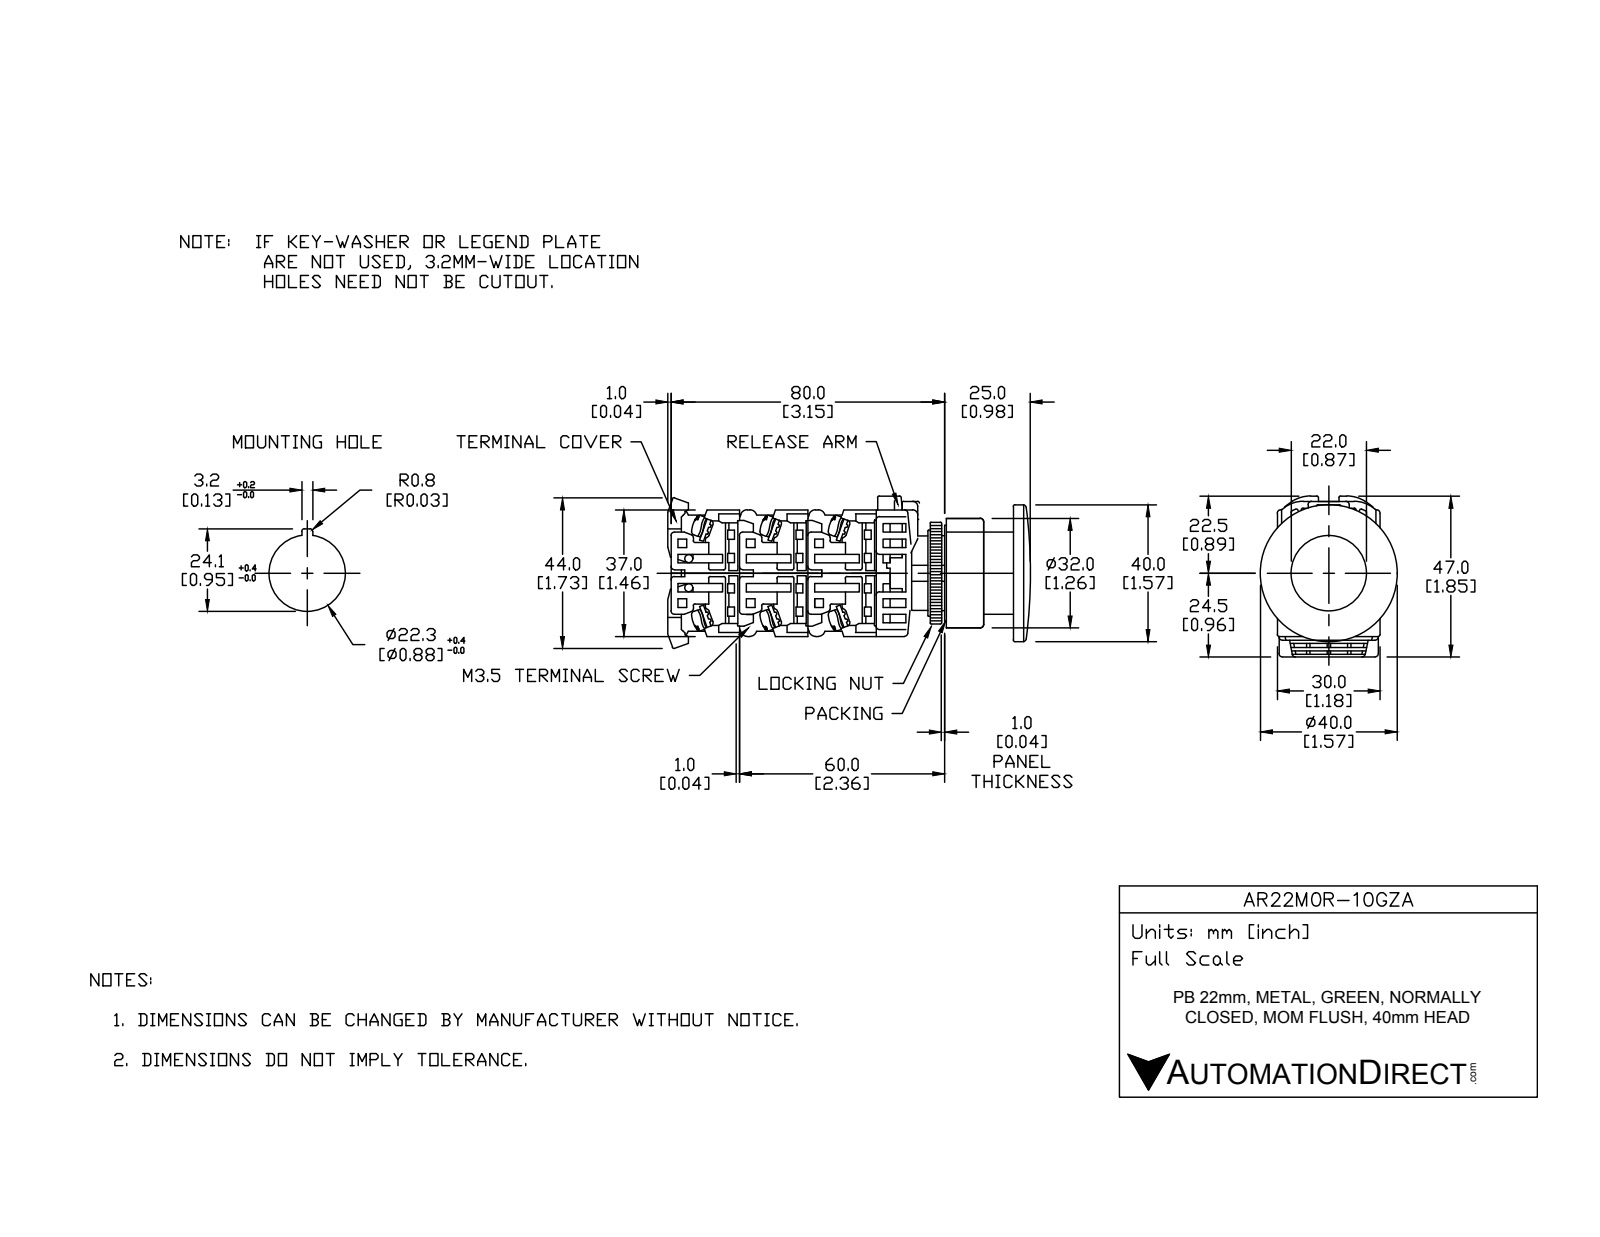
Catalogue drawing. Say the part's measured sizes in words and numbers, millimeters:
The part is named "AR22M0R-10GZA". Its 3-D file was written by "SolidWorks 2017 (AUTOMOTIVE_DESIGN)". It is 12 solids with 304 faces: 202 planar, 76 cylindrical and 26 other. Overall it measures 66.5 by 43 by 40 millimeters. Its volume is 37 326 cubic millimeters and its surface area 22 079 square millimeters. Round holes: 1 of diameter 21.8, 1 of diameter 22, 1 of diameter 25, 1 of diameter 31. Round bosses or shafts: 2 of diameter 5, 1 of diameter 40, 1 of diameter 32, 1 of diameter 30.5, 1 of diameter 29.8, 1 of diameter 24, 1 of diameter 23.8, 1 of diameter 21.75. Partial cylindrical surfaces (rounded edges, fillets, slot ends): 23 of radius 0.5, 4 of radius 1.75, 4 of radius 5, 2 of radius 4, 1 of radius 16.59, 1 of radius 17.59. The main face-to-face distances are 1, 10, 28.5, 18, 38.5, 21, 3, 2, 29, 7.5.
